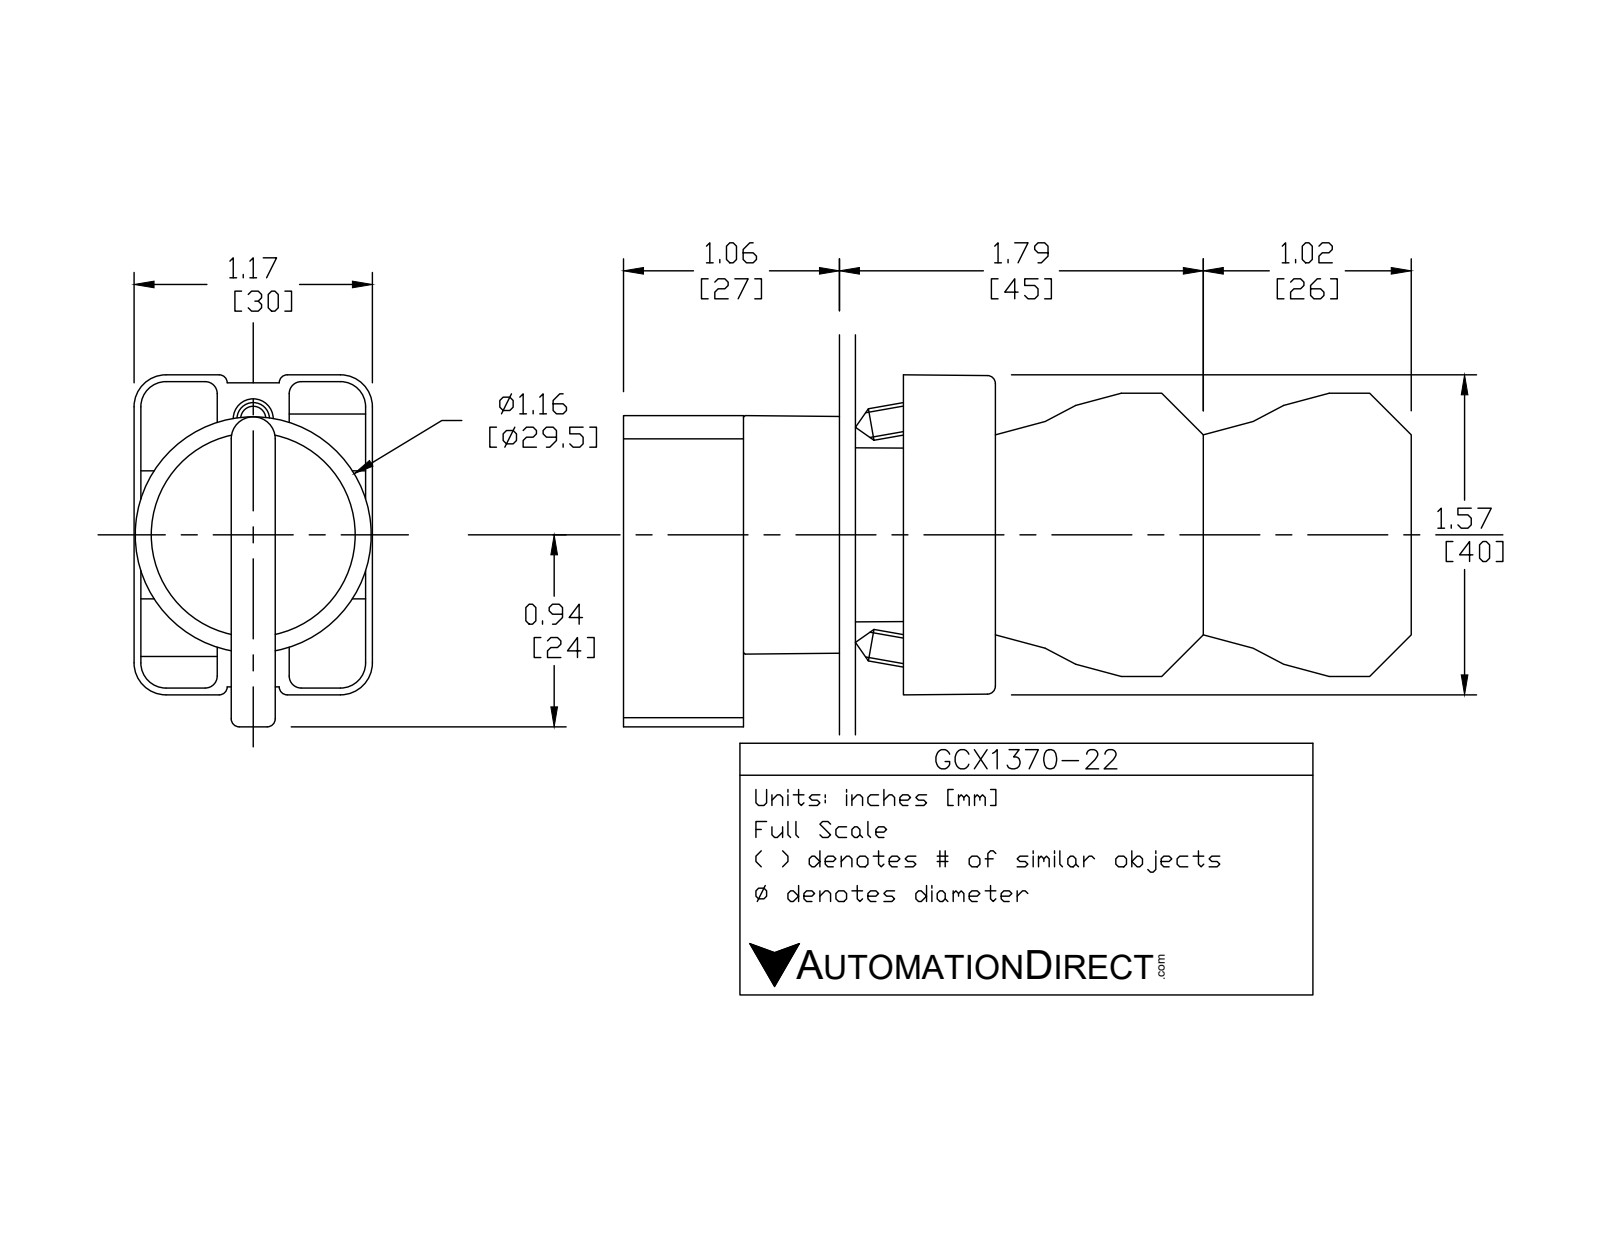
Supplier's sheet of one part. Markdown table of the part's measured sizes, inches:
| quantity | value |
| --- | --- |
| part name | GCX1370-22; ecx1029; GCX1370 OPERATOR; ecx1030 (+1 more) |
| STEP written by | SolidWorks 2016 (AUTOMOTIVE_DESIGN) |
| units | inches |
| bodies | 9 solids, 675 faces (457 planar, 179 cylindrical, 39 other) |
| overall size | 3.803 × 1.752 × 1.177 |
| volume | 3.881 in³ |
| surface area | 49.46 in² |
| round holes (diameter × count) | 0.079 × 4, 0.087 × 2, 0.124 × 2, 0.13 × 2, 0.197 × 1, 0.878 × 1, 0.888 × 1, 1.024 × 1 |
| round bosses / shafts (diameter × count) | 0.157 × 2, 1.175 × 1, 1.004 × 1, 0.945 × 1, 0.856 × 1, 0.78 × 1 |
| partial cylindrical surfaces (radius × count) | 0.059 × 24, 0.041 × 12, 0.124 × 12, 0.157 × 12, 0.039 × 6, 0.02 × 2, 0.063 × 2, 0.079 × 2 |
| main face-to-face distances | 0.598, 0.579, 1.024, 1.177, 0.02, 1.744, 0.124, 0.72, 0.474, 0.703 |
| hole center spacings | 0.236, 0.544, 1.008, 0.98, 0.472, 0.49, 1.088 |
